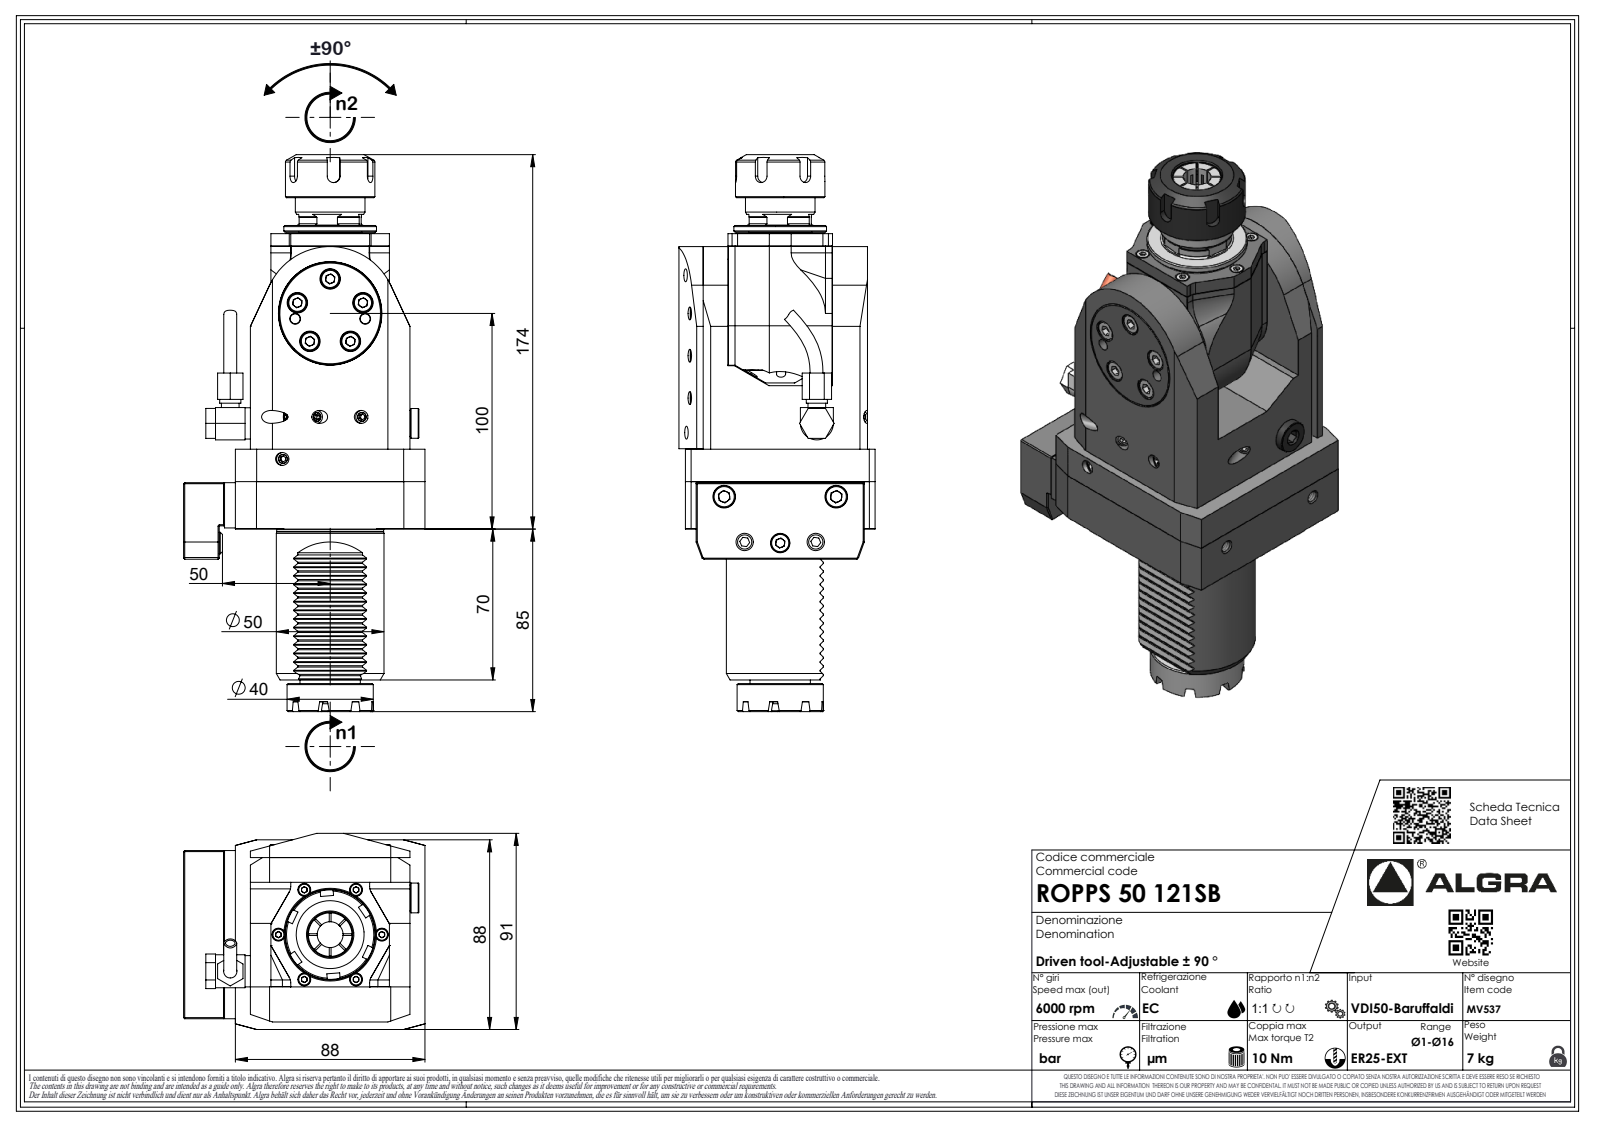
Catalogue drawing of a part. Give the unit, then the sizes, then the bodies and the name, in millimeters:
Units: millimetres
Overall size (bounding box): 257.65 × 112 × 91
Round holes (diameter × count): ⌀2.1 ×1
Round bosses / shafts (diameter × count): ⌀50 ×1, ⌀49.6 ×1, ⌀43 ×1, ⌀41.5 ×1, ⌀41 ×1, ⌀40 ×1, ⌀32.3 ×1, ⌀29.3 ×1
Partial cylindrical surfaces — rounded edges, fillets, slot ends (radius × count): R0.2 ×17, R0.3 ×15, R0.33 ×7, R0.52 ×7, R3.7 ×7, R3 ×5, R5.1 ×4, R20 ×2
Main face-to-face distances: 7, 81, 88, 19.75, 68.25, 84.5, 74, 16.5, 112, 105
Volume: 1 011 000 mm³ · Surface area: 96 989 mm²
Bodies: 1 solid, 710 faces (454 planar, 109 cylindrical, 147 other)
Part name (STEP PRODUCT): ROPPS50121SB
STEP written by: SolidWorks 2023 (AUTOMOTIVE_DESIGN)
